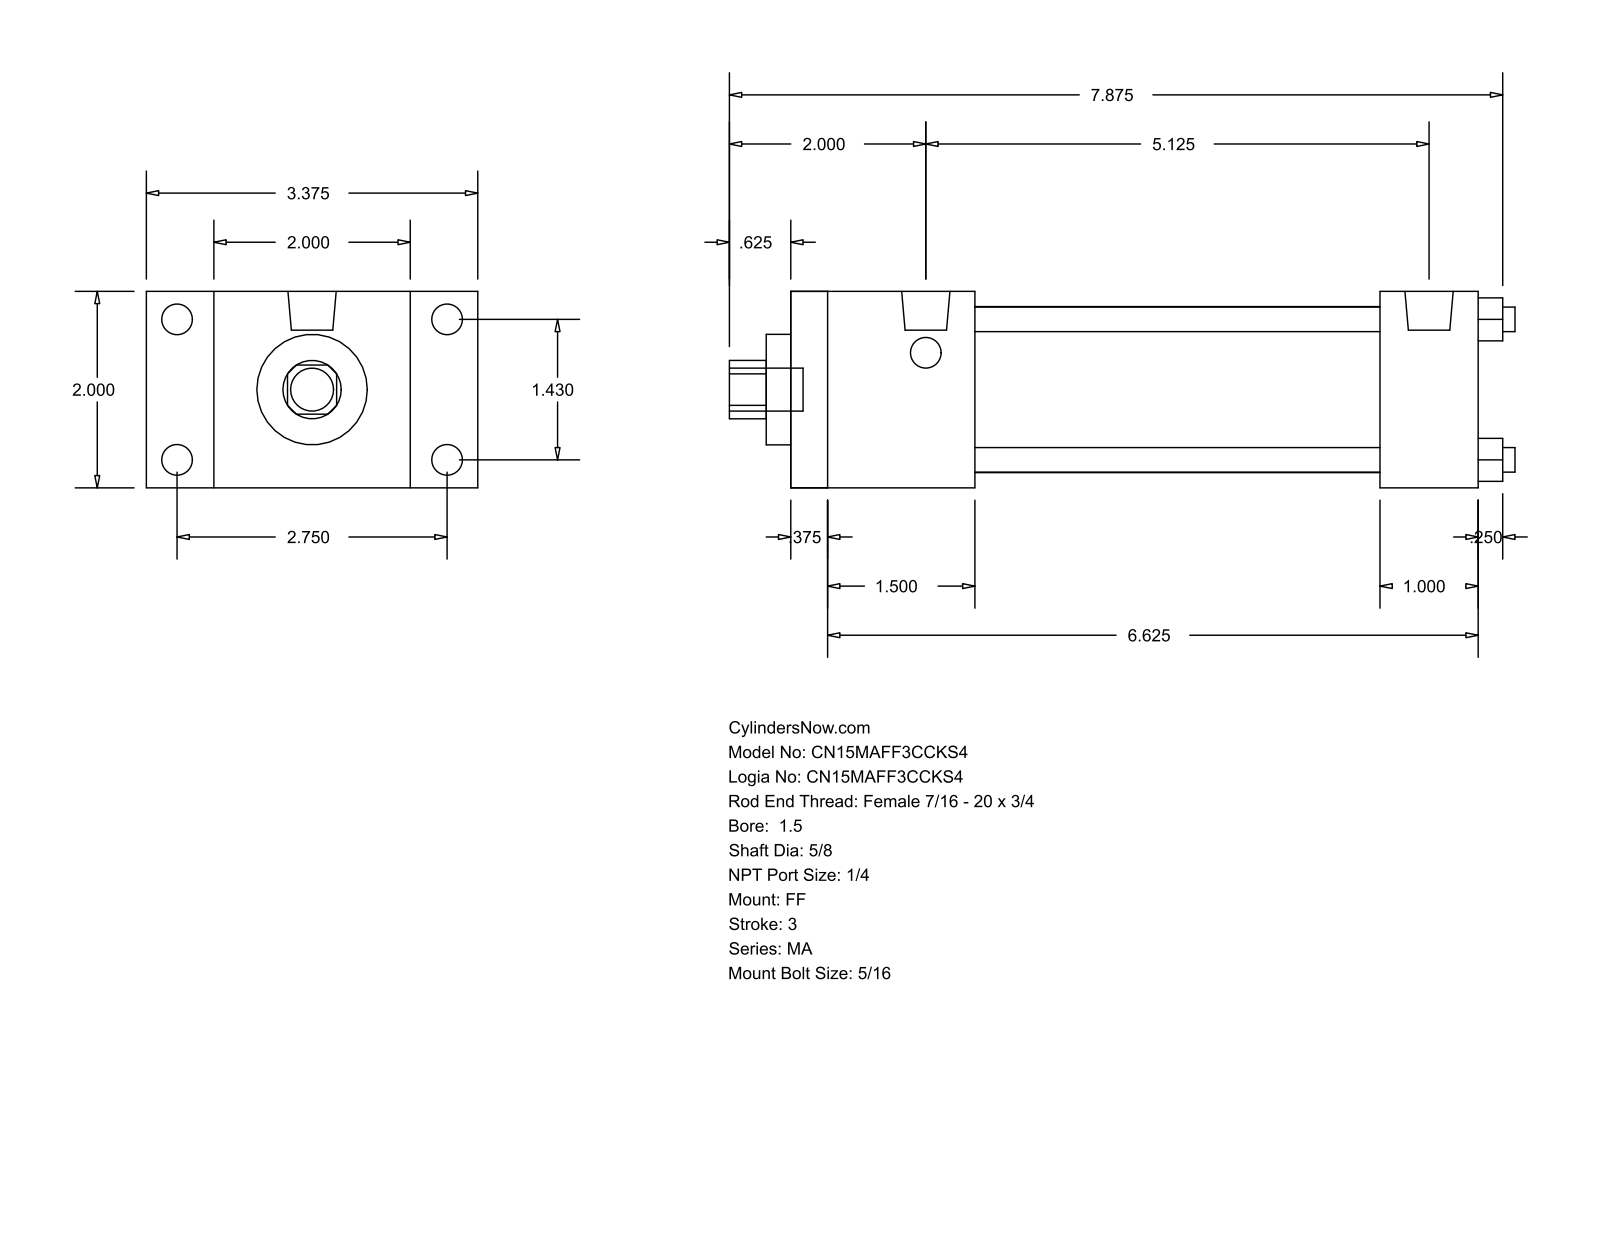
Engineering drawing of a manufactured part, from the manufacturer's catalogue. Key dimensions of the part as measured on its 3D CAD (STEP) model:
Part name (STEP PRODUCT): MA_FF__0150_0.625
STEP written by: GSSL Pune (CONFIG_CONTROL_DESIGN)
Units: millimetres
Bodies: 0 solids, 92 faces (64 planar, 28 cylindrical, 0 other)
Overall size (bounding box): 203.2 × 85.72 × 50.8
Round holes (diameter × count): ⌀6.35 ×4, ⌀15.88 ×1, ⌀28.57 ×1, ⌀42.93 ×1
Round bosses / shafts (diameter × count): ⌀7.94 ×8, ⌀12.49 ×2, ⌀11.11 ×1
Partial cylindrical surfaces — rounded edges, fillets, slot ends (radius × count): R7.54 ×1
Main face-to-face distances: 50.8, 177.8, 9.52, 168.28, 25.4, 47.62, 152.4, 38.1, 142.88, 104.78
Hole centre spacings: 25.68, 36.32, 51.36
